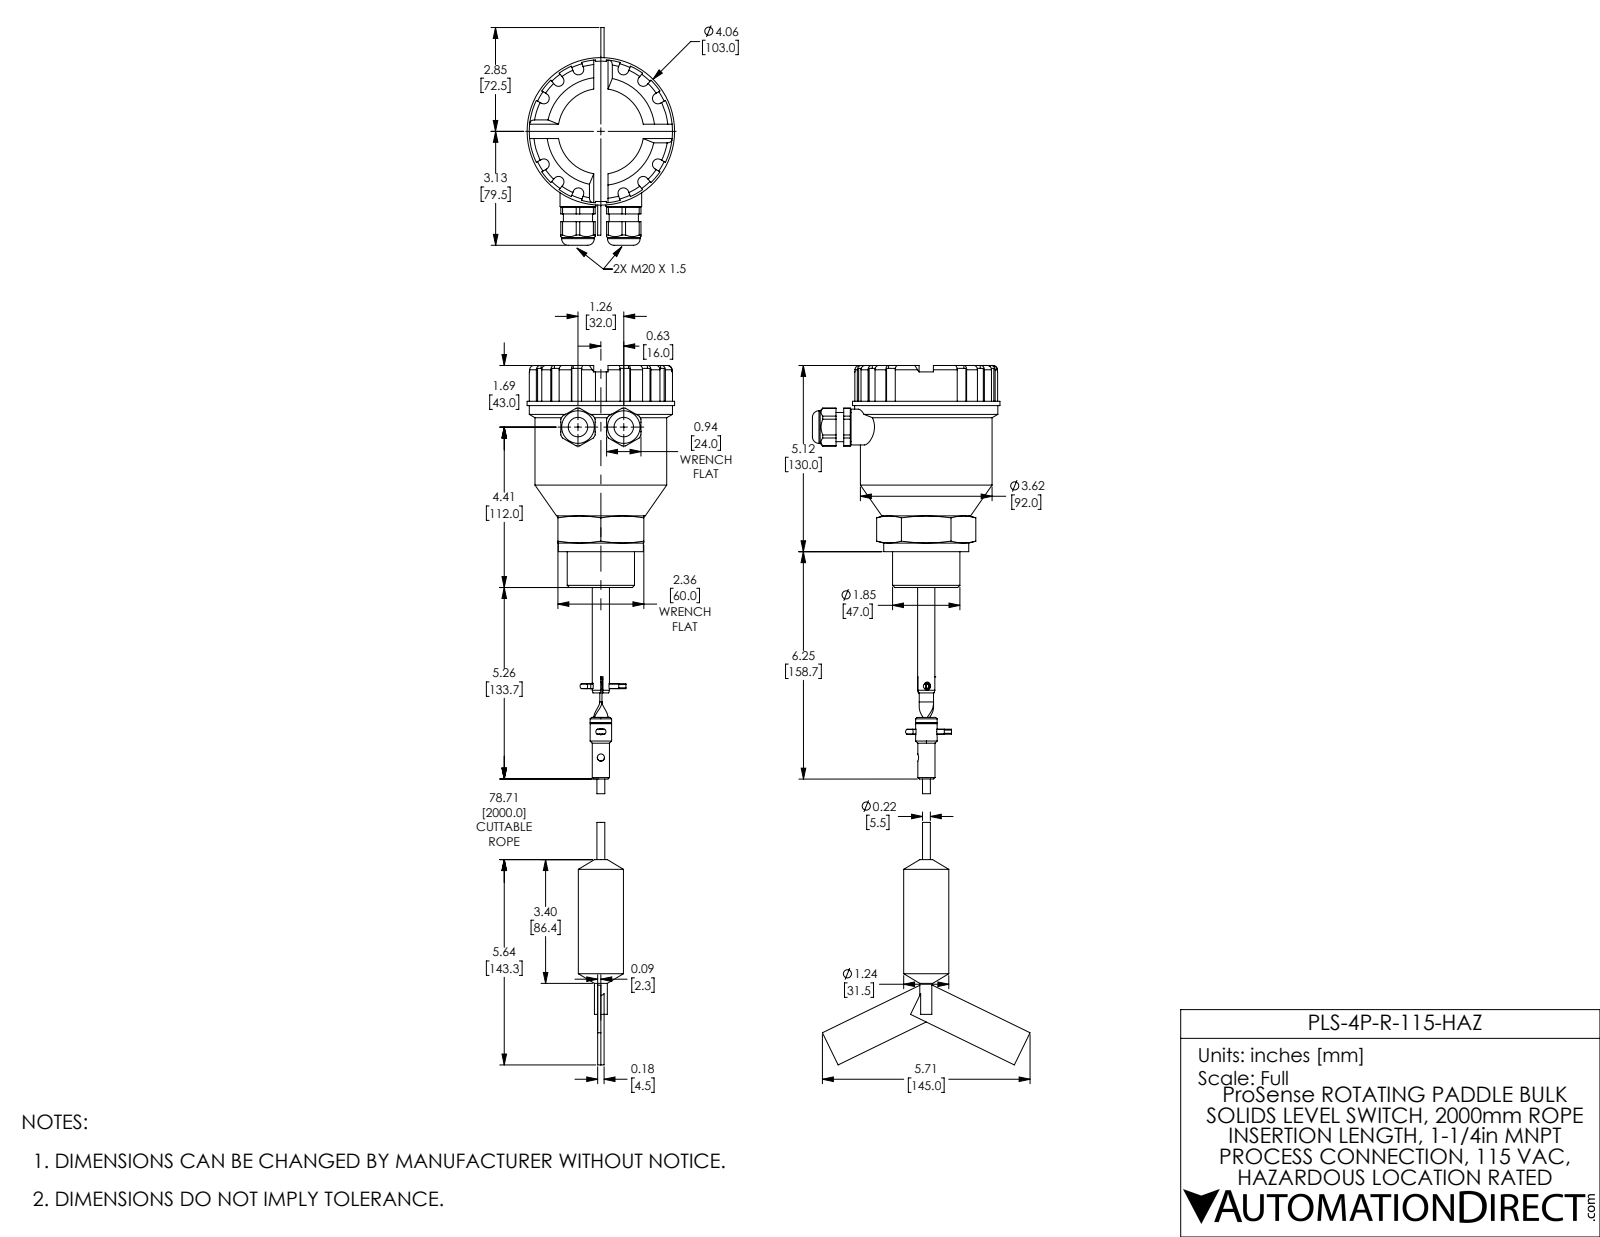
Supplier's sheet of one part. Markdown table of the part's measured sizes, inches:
| quantity | value |
| --- | --- |
| part name | PLS-4P-R-115 fxt |
| STEP written by | SolidWorks 2017 (AUTOMOTIVE_DESIGN) |
| units | inches |
| bodies | 5 solids, 628 faces (244 planar, 289 cylindrical, 95 other) |
| overall size | 19.225 × 5.984 × 4.055 |
| volume | 56.54 in³ |
| surface area | 170.5 in² |
| round holes (diameter × count) | 0.157 × 10, 0.126 × 8, 0.098 × 4, 0.161 × 2, 0.159 × 1, 0.181 × 1, 0.197 × 1, 0.354 × 1, 0.476 × 1, 0.866 × 1, 1.102 × 1 |
| round bosses / shafts (diameter × count) | 0.984 × 2, 0.898 × 2, 0.803 × 2, 0.472 × 2, 0.217 × 2, 4.055 × 1, 3.937 × 1, 3.622 × 1 |
| partial cylindrical surfaces (radius × count) | 0.024 × 16, 0.15 × 12, 0.079 × 8, 0.079 × 4, 0.069 × 2, 0.52 × 2, 0.709 × 1, 0.866 × 1 |
| main face-to-face distances | 0.177, 0.089, 4.114, 2.362, 0.984, 5.118, 4.291, 0.315, 1.093, 1.181 |
| hole center spacings | 0.603, 0.787, 1.113, 1.455, 1.574, 1.575, 5.154, 5.327 |
